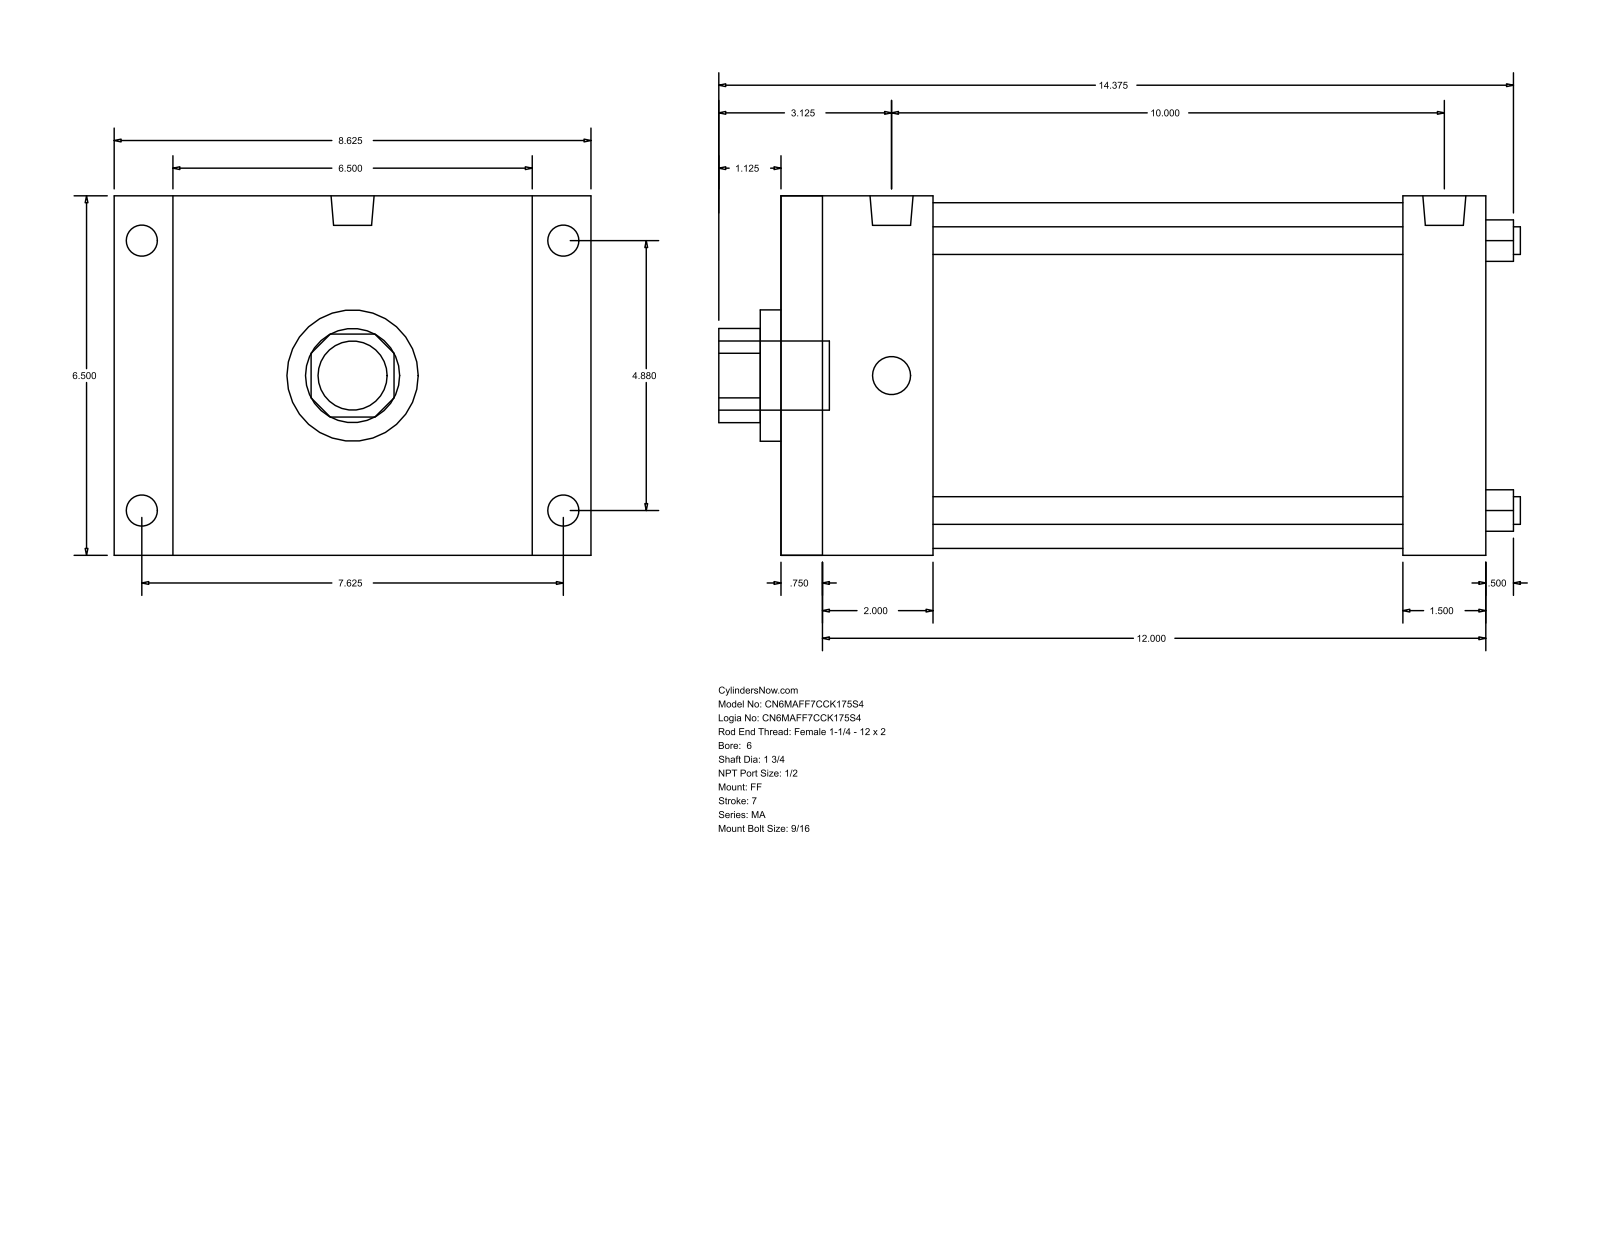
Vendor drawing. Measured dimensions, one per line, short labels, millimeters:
name: MA_FF__0600_1.75
written by: GSSL Pune (CONFIG_CONTROL_DESIGN)
unit: mm
bodies: 0 solids, 92 faces (64 planar, 28 cylindrical, 0 other)
size: 368.3 × 219.07 × 165.1
holes: 4× ⌀12.7, 1× ⌀44.45, 1× ⌀60.33, 1× ⌀158.75
bosses: 4× ⌀17.46, 4× ⌀14.29, 2× ⌀19.77, 1× ⌀31.75
rounds: 1× R21.63
face distances: 165.1, 323.86, 19.05, 304.81, 50.8, 266.7, 69.85, 254.01, 285.75, 215.9
hole spacings: 87.65, 123.96, 175.31
